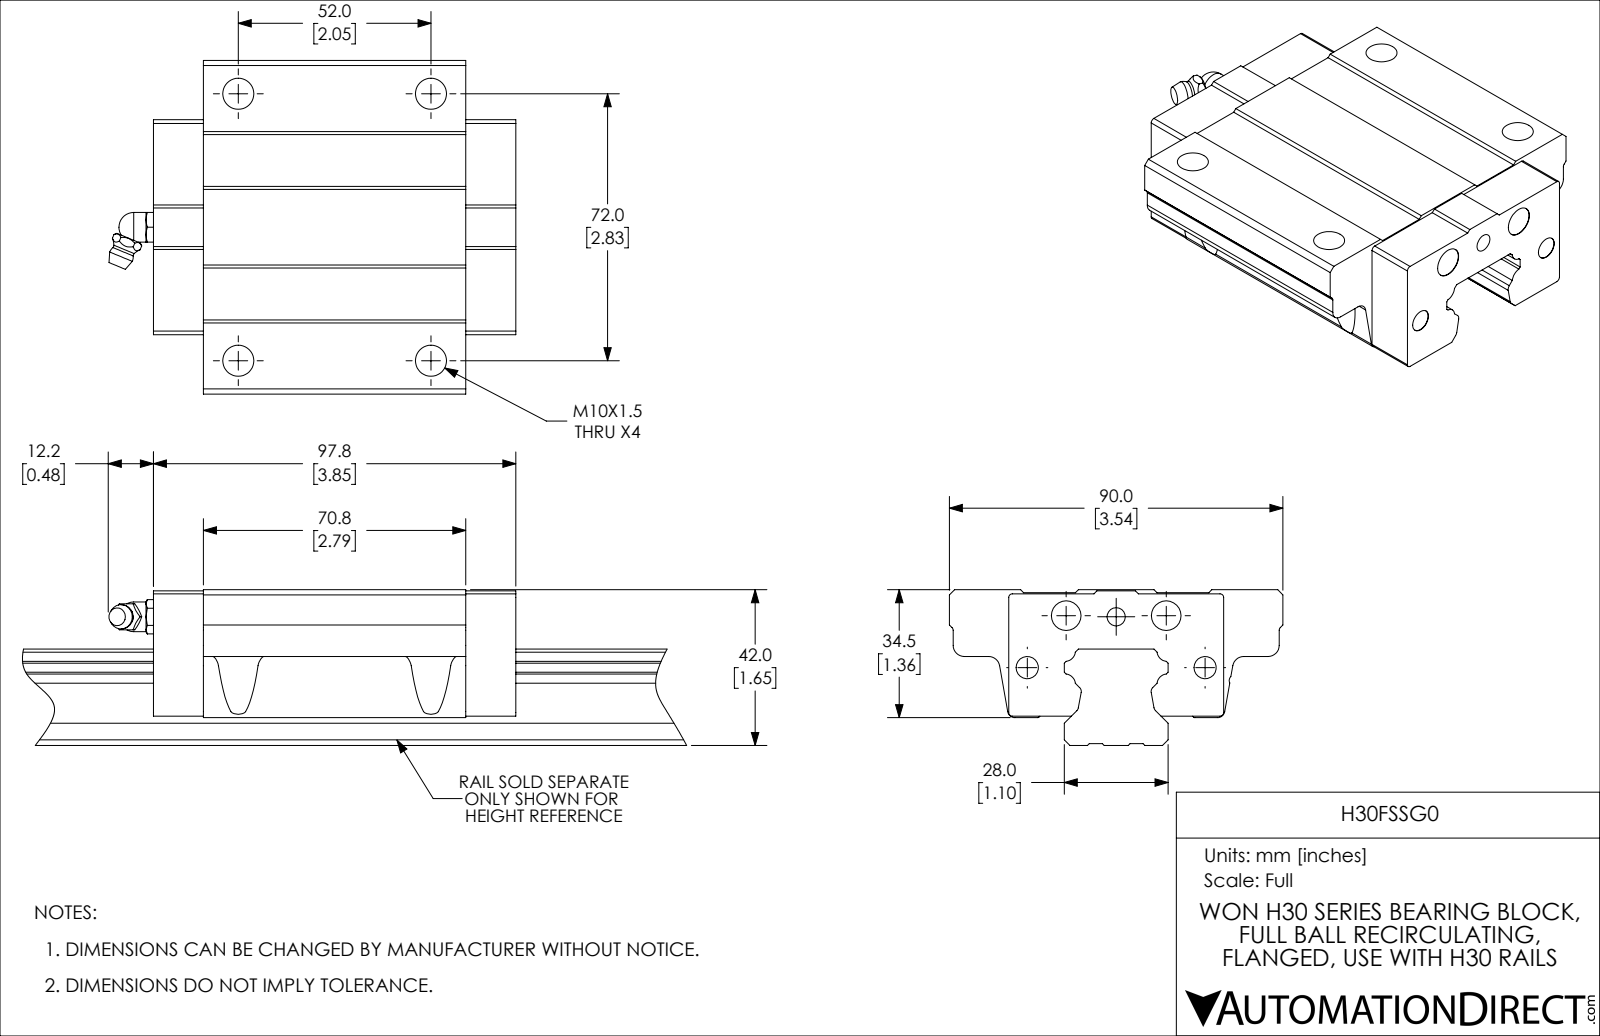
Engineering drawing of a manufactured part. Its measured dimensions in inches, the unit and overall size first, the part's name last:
Units: inches
Overall size (bounding box): 4.323 × 3.543 × 1.358
Round holes (diameter × count): ⌀0.33 ×4, ⌀0.236 ×2, ⌀0.315 ×2, ⌀0.194 ×1
Round bosses / shafts (diameter × count): ⌀0.315 ×1, ⌀0.236 ×1
Partial cylindrical surfaces — rounded edges, fillets, slot ends (radius × count): R0.039 ×6, R0.059 ×5, R0.11 ×4, R0.118 ×4, R0.276 ×4, R0.02 ×2, R0.079 ×2
Main face-to-face distances: 0.63, 0.031, 1.343, 0.713, 1.311, 0.598, 3.85, 2.283, 0.531, 3.319
Hole centre spacings: 0.531, 0.689, 1.088, 1.576, 2.047, 2.835, 3.496, 1.063
Volume: 11.55 in³ · Surface area: 50.37 in²
Bodies: 2 solids, 188 faces (97 planar, 69 cylindrical, 22 other)
Part name (STEP PRODUCT): H30FSSG0
STEP written by: SolidWorks 2019 (CONFIG_CONTROL_DESIGN)
